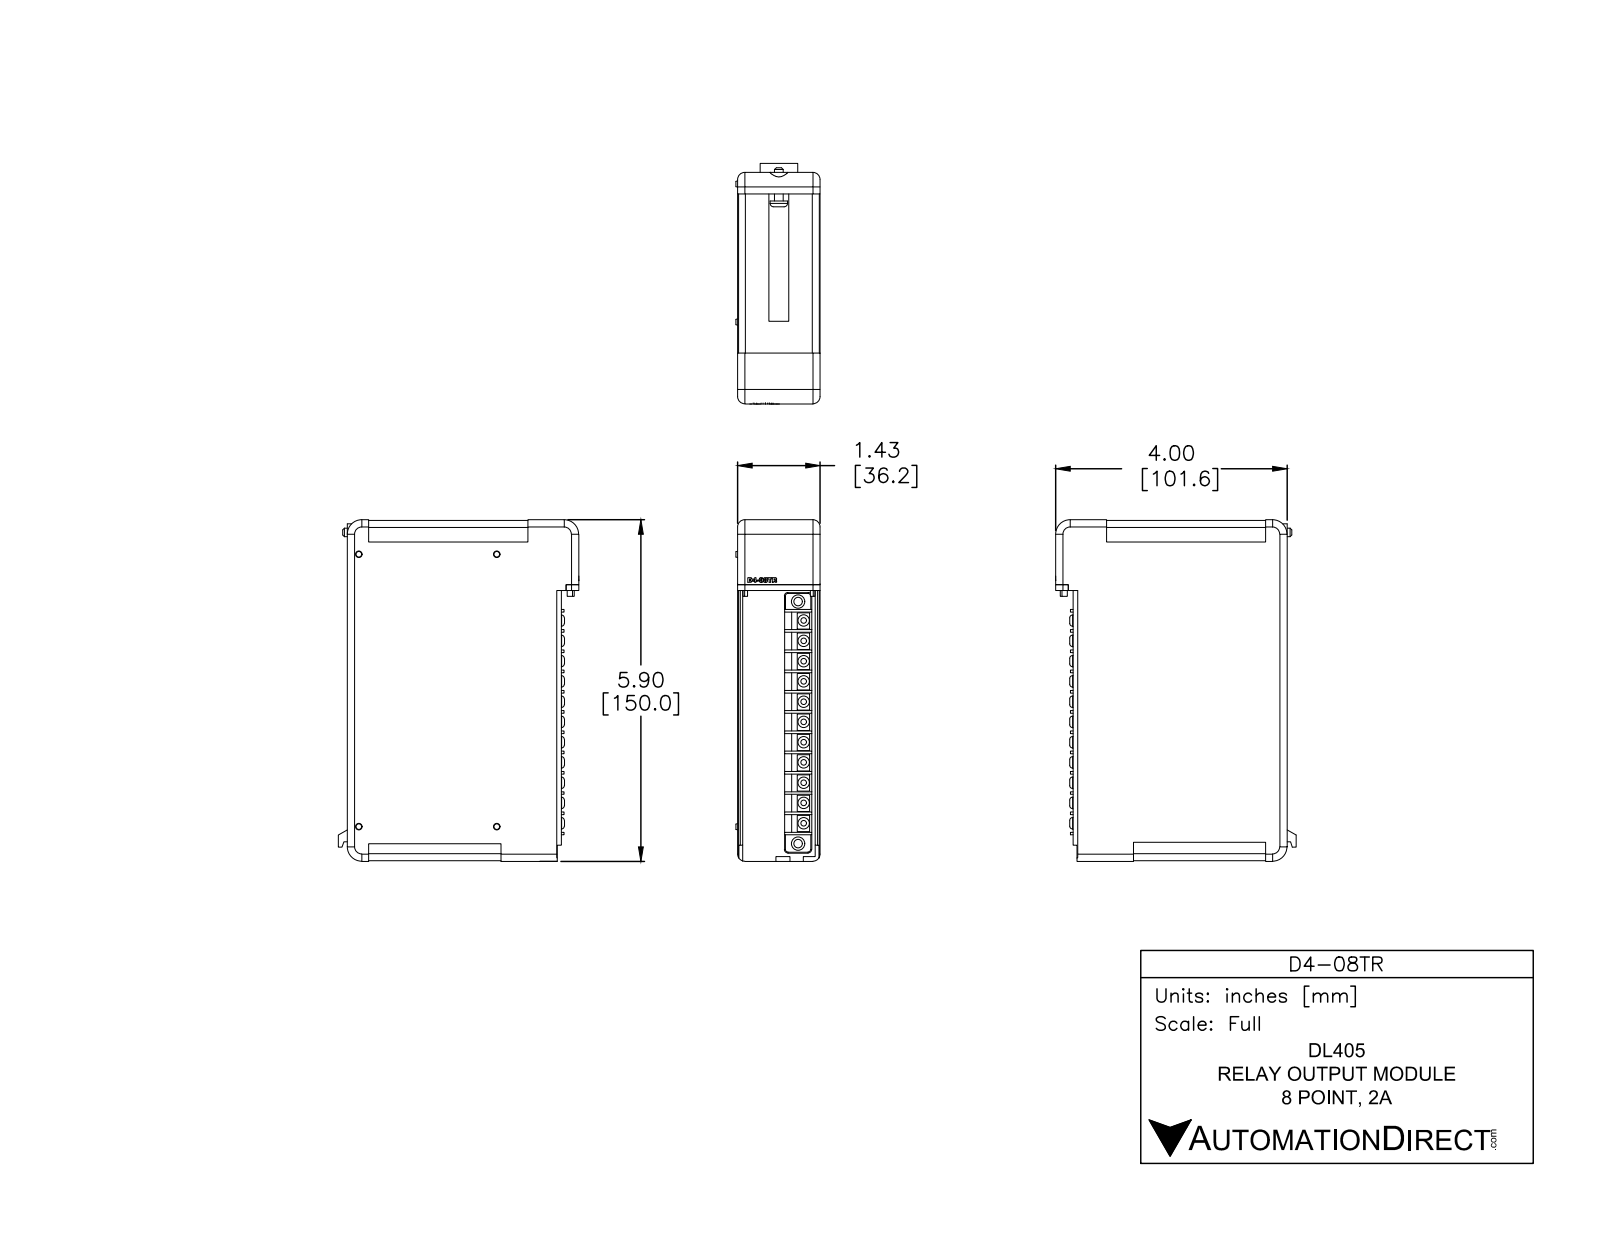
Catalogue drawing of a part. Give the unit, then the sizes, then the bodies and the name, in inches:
Units: inches
Overall size (bounding box): 5.905 × 4.156 × 1.455
Round bosses / shafts (diameter × count): ⌀0.2 ×11, ⌀0.229 ×2, ⌀0.3 ×1, ⌀0.15 ×1
Partial cylindrical surfaces — rounded edges, fillets, slot ends (radius × count): R0.125 ×8, R0.015 ×6, R0.06 ×4, R0.12 ×4, R0.25 ×3, R0.03 ×2, R0.151 ×1, R0.171 ×1
Main face-to-face distances: 1.425, 0.015, 3.325, 0.085, 1.34, 5.875, 0.07, 0.2, 1.41, 1.325
Volume: 29.11 in³ · Surface area: 85.81 in²
Bodies: 10 solids, 449 faces (291 planar, 71 cylindrical, 87 other)
Part name (STEP PRODUCT): D4-08TR
STEP written by: SolidWorks 2014 (AUTOMOTIVE_DESIGN)
